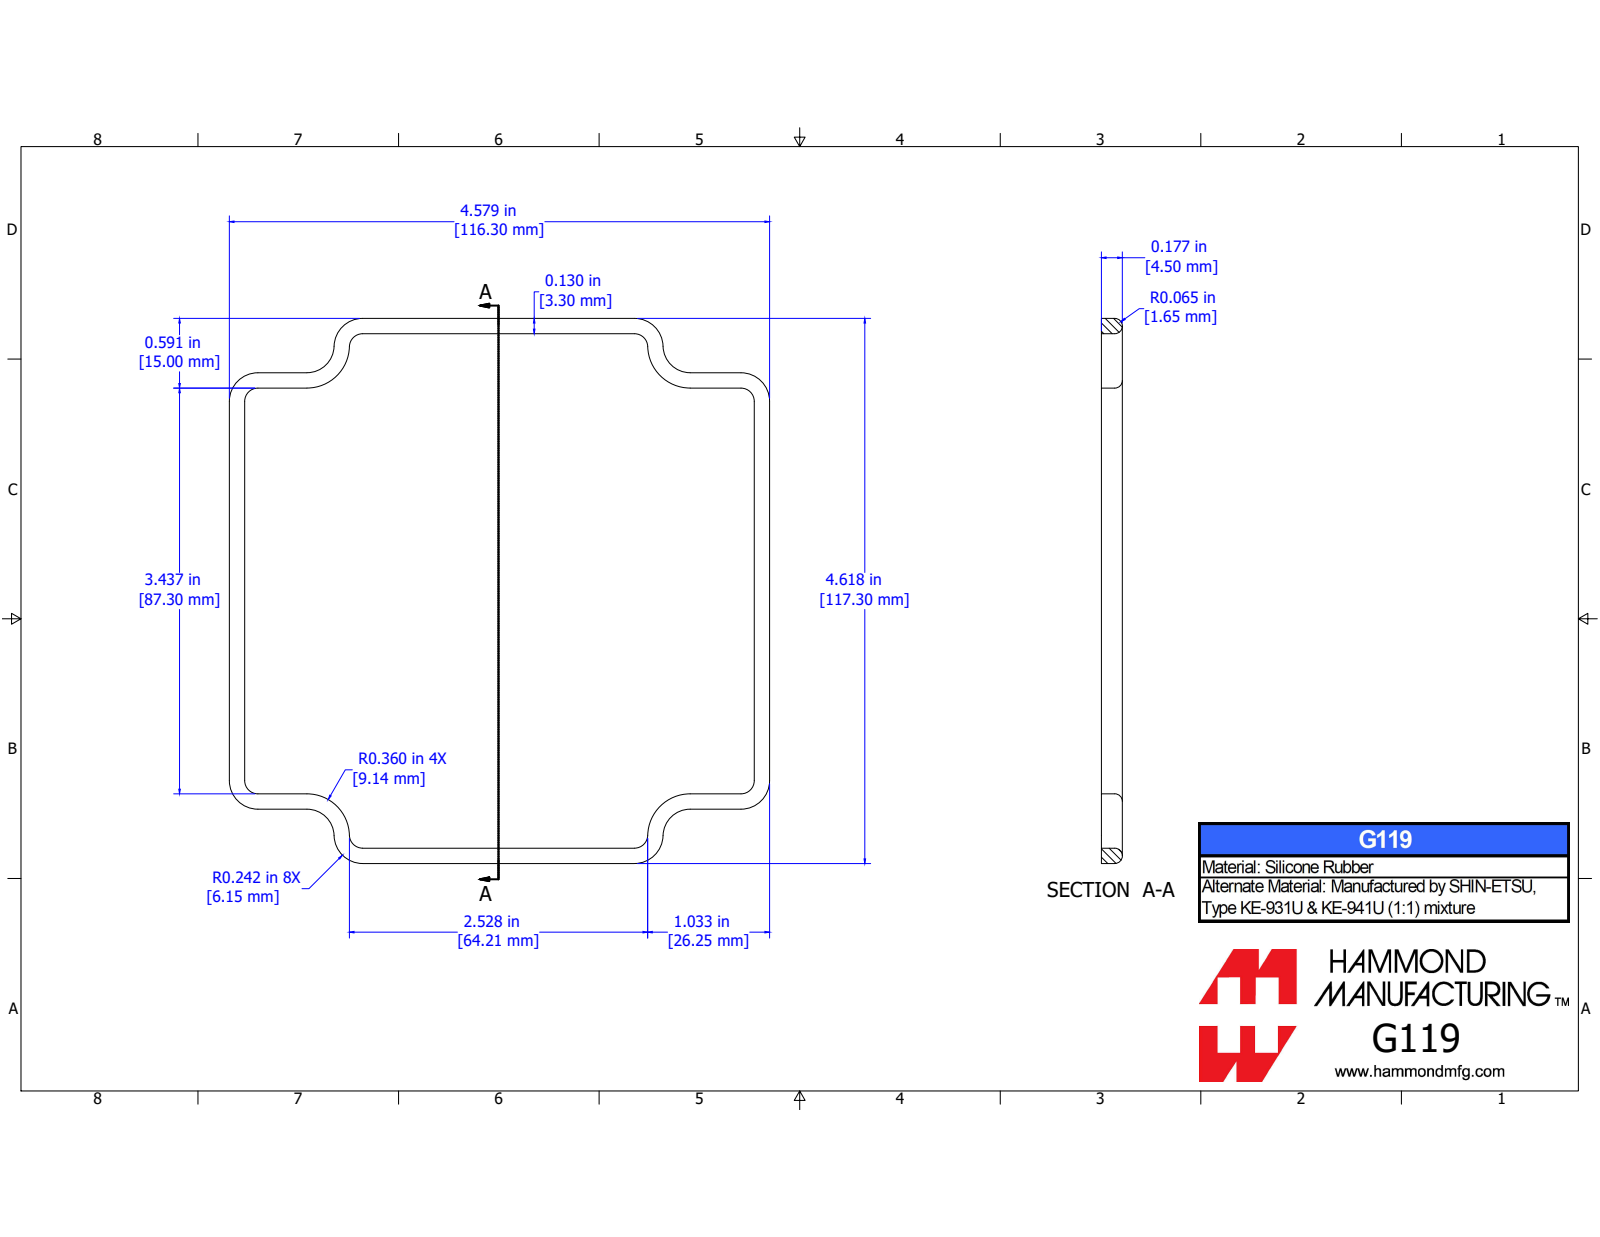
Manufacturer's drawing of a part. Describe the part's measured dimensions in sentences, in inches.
The part is named "1590Z119G". Its 3-D file was written by "SolidWorks 2019 (CONFIG_CONTROL_DESIGN)". It is 1 solid with 82 faces: 18 planar, 16 cylindrical and 48 other. Overall it measures 4.644 by 4.565 by 0.177 inches. Its volume is 0.356 cubic inches and its surface area 9.551 square inches. Partial cylindrical surfaces (rounded edges, fillets, slot ends): 12 of radius 0.039. The main face-to-face distances are 4.439, 0.177, 4.518, 0.453, 4.065, 3.612.
